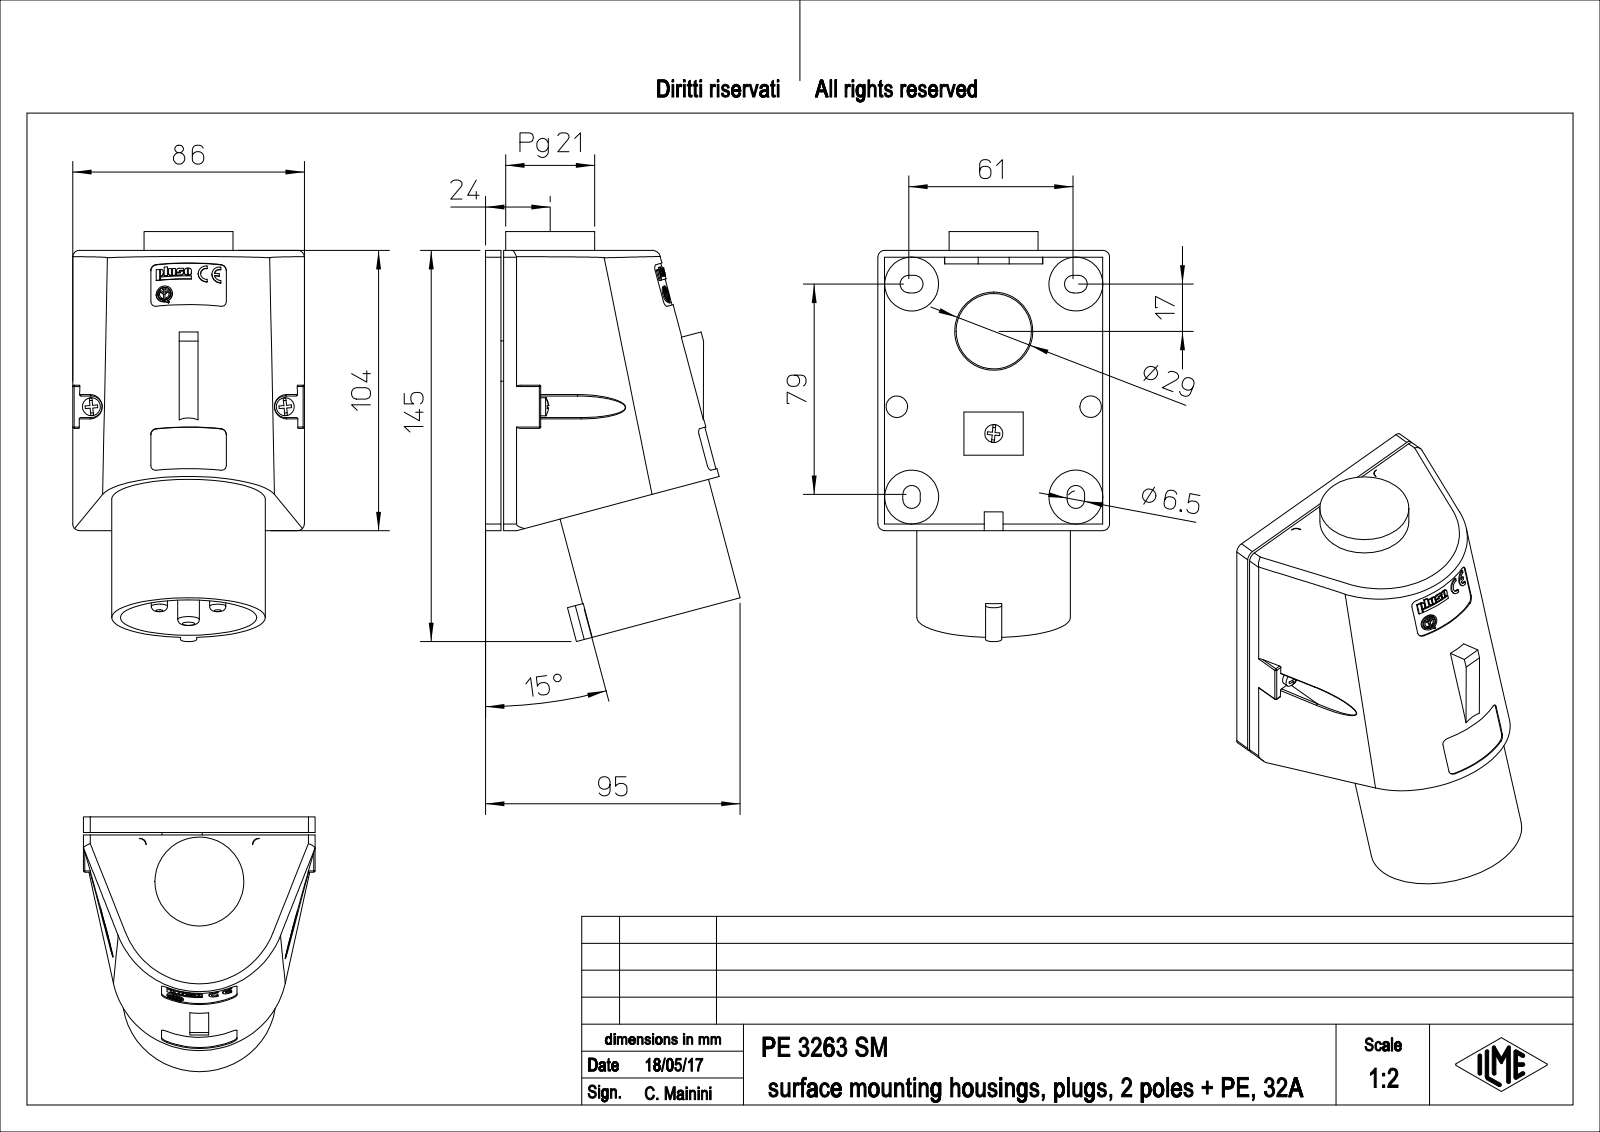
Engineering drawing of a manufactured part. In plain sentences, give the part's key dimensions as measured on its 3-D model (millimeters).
The part is named "PE_3263_SM". Its 3-D file was written by "PTC Creo Elements/Direct Modeling 19.0E 27-Jun-2016 (C) Parametric Technology GmbH (AUTOMOTIVE_DESIGN)". It is 1 solid with 1004 faces: 657 planar, 213 cylindrical and 134 other. Overall it measures 152.14 by 94.53 by 86 millimeters. Its volume is 491 313 cubic millimeters and its surface area 90 882 square millimeters. Round holes: 2 of diameter 2.8, 2 of diameter 3.2, 2 of diameter 4, 2 of diameter 4.5, 2 of diameter 6.1, 1 of diameter 4.2, 1 of diameter 5.04, 1 of diameter 27.54, 1 of diameter 29, 1 of diameter 32, 1 of diameter 50.6. Round bosses or shafts: 5 of diameter 6.7, 4 of diameter 20, 3 of diameter 8, 3 of diameter 6, 2 of diameter 3, 1 of diameter 57, 1 of diameter 50, 1 of diameter 33. Partial cylindrical surfaces (rounded edges, fillets, slot ends): 22 of radius 0.5, 11 of radius 0.17, 10 of radius 2, 9 of radius 0.86, 8 of radius 3.25, 6 of radius 2.5, 4 of radius 0.3, 4 of radius 4.5. The main face-to-face distances are 0.98, 4.75, 5.73, 1, 7, 5.75, 6.73, 2.25, 2.5, 8. The hole center spacings are 12.51, 21, 37.36, 45.61, 72, 11.94, 21.66, 23.48.
